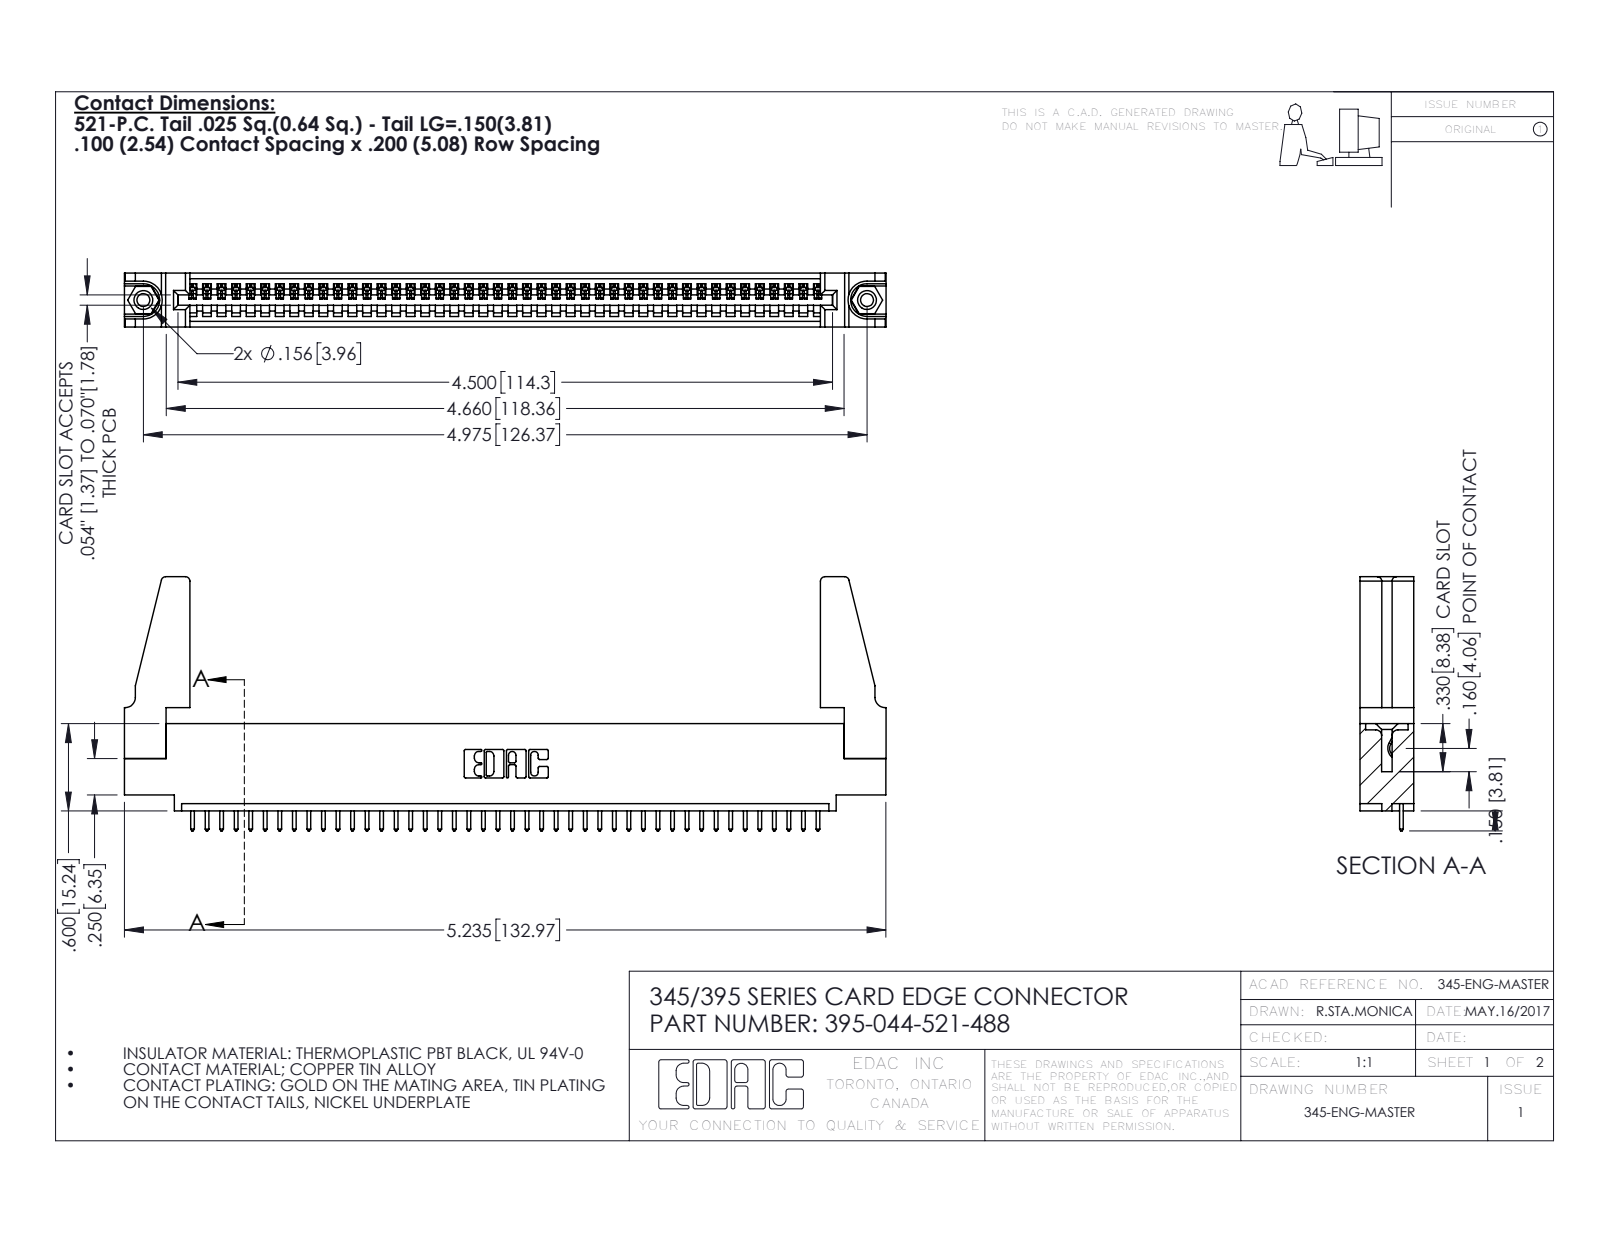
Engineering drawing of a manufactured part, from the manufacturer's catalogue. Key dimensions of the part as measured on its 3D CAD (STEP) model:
Part name (STEP PRODUCT): 345-250-001_345-250-001-102; 345-220-078_345-220-088; 345-292-001_345-293-121; 345 Part_0.110 Offset - 0.156 Dia-TH (+1 more)
STEP written by: SolidWorks 2016 (CONFIG_CONTROL_DESIGN)
Units: inches
Bodies: 49 solids, 2806 faces (1916 planar, 874 cylindrical, 16 other)
Overall size (bounding box): 5.236 × 1.747 × 0.37
Volume: 0.958 in³ · Surface area: 29.9 in²
Round holes (diameter × count): ⌀0.089 ×2, ⌀0.125 ×2, ⌀0.156 ×2, ⌀0.064 ×1
Round bosses / shafts (diameter × count): ⌀0.155 ×2
Partial cylindrical surfaces — rounded edges, fillets, slot ends (radius × count): R0.006 ×88, R0.01 ×88, R0.01 ×22, R0.03 ×8, R0.007 ×6, R0.031 ×6, R0.026 ×3, R0.031 ×2
Main face-to-face distances: 0.072, 0.298, 0.37, 0.2, 0.098, 0.272, 0.025, 0.225, 0.149, 0.072
Hole centre spacings: 0.27, 4.739, 4.975
